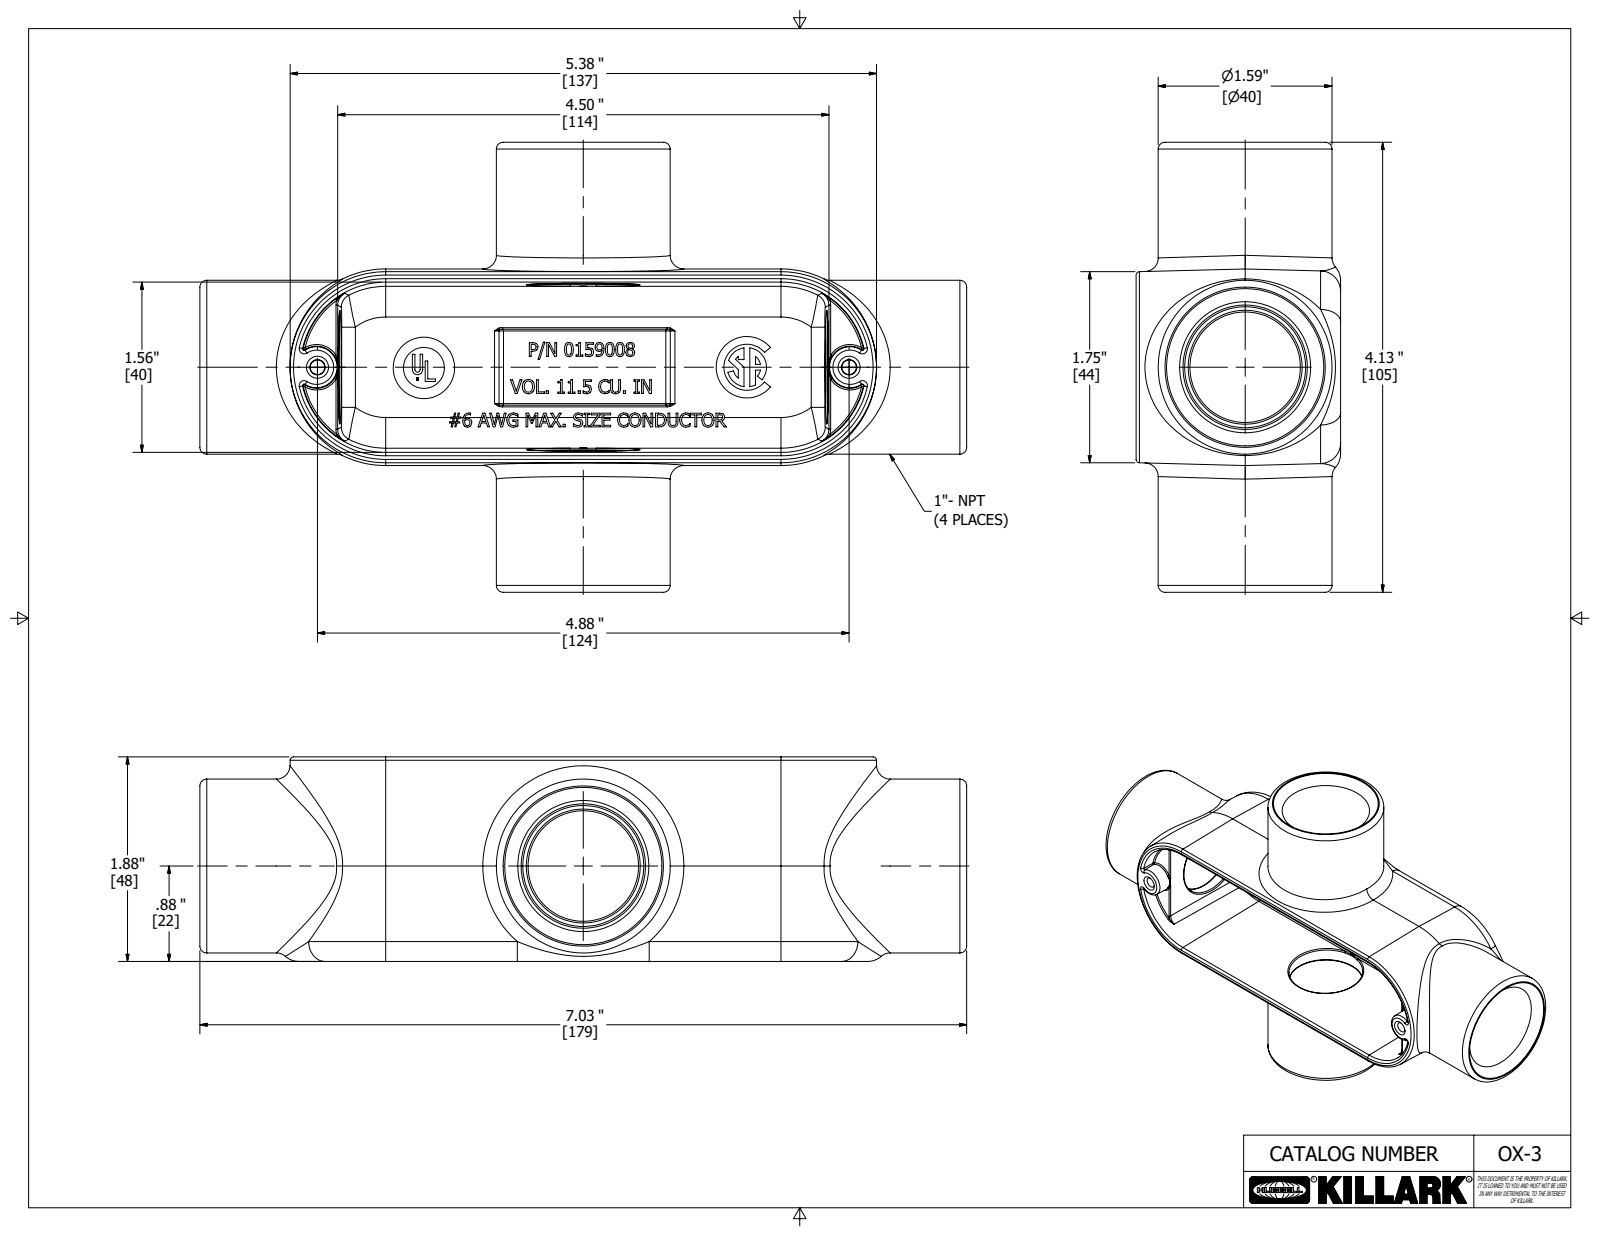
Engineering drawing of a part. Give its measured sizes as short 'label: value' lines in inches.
name: 11714-1
written by: Autodesk Inventor 2018 (AUTOMOTIVE_DESIGN)
unit: in
bodies: 1 solid, 1113 faces (581 planar, 69 cylindrical, 463 other)
size: 7.031 × 4.125 × 1.875
volume: 7.591 in³; area: 91.57 in²
holes: 2× ⌀1.013, 1× ⌀0.375
bosses: 2× ⌀1.594, 1× ⌀0.563
rounds: 12× R0.031, 4× R0.015, 4× R0.062, 2× R0.016, 2× R0.125, 2× R0.187, 2× R0.281, 1× R0.023
face distances: 1.656, 0.094, 1.802, 0.146, 0.031, 0.125, 0.063, 1.875, 1.844, 1.781
